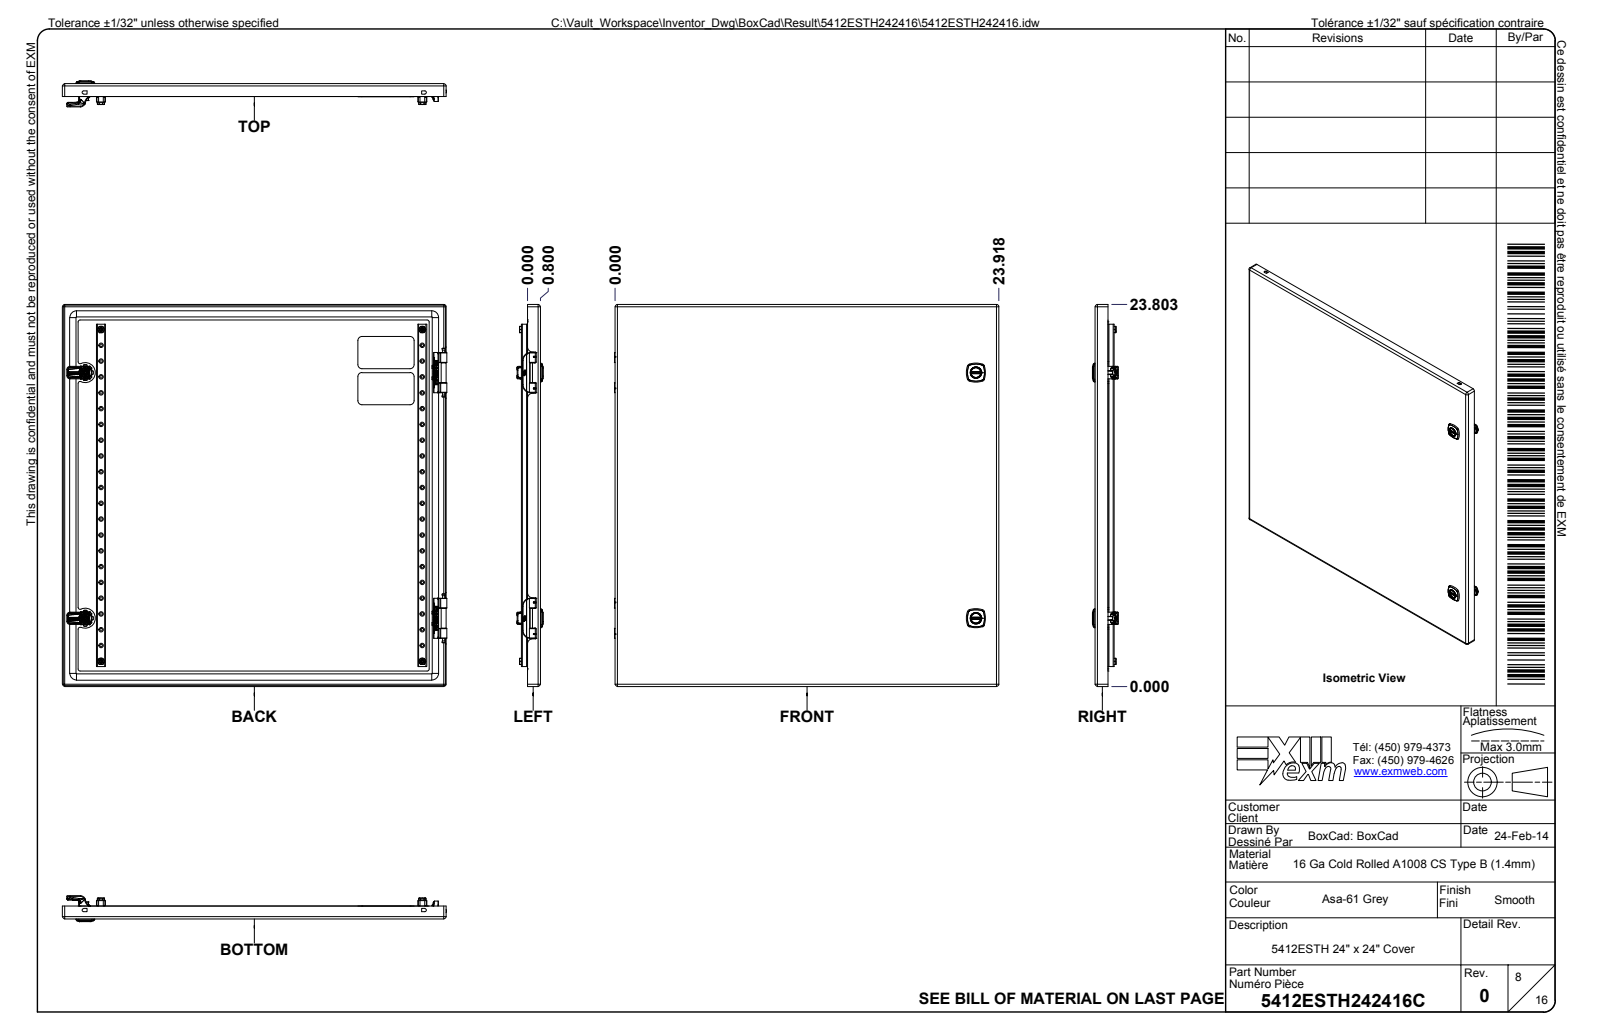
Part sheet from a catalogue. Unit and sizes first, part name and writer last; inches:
Units: inches
Overall size (bounding box): 26.25 × 24.003 × 17.603
Round holes (diameter × count): ⌀0.165 ×40, ⌀0.03 ×10, ⌀0.201 ×10, ⌀0.5 ×10, ⌀0.043 ×8, ⌀0.311 ×6, ⌀0.394 ×6, ⌀0.406 ×6, ⌀0.178 ×4, ⌀0.268 ×4, ⌀0.29 ×4, ⌀0.335 ×4
Round bosses / shafts (diameter × count): ⌀0.237 ×40, ⌀0.232 ×10, ⌀0.03 ×10, ⌀0.256 ×8, ⌀0.039 ×8, ⌀0.289 ×6, ⌀0.177 ×6, ⌀0.748 ×4
Partial cylindrical surfaces — rounded edges, fillets, slot ends (radius × count): R0.02 ×299, R0.008 ×182, R0.01 ×163, R0.039 ×77, R0.125 ×52, R0.012 ×50, R0.031 ×46, R0.059 ×37
Main face-to-face distances: 0.053, 0.75, 0.803, 23.144, 23.894, 23.947, 23.197, 17.081, 17.028, 16.331
Hole centre spacings: 1.969, 21.405, 0.984, 2.953, 15.303, 3.937, 20.25, 20.25
Volume: 2 056 in³ · Surface area: 12 634 in²
Bodies: 87 solids, 14321 faces (4447 planar, 3913 cylindrical, 5961 other)
Part name (STEP PRODUCT): 5412ESTH242416; 5412ESTH242416B; 5412ESTH242416B-P; STK-Q-16005 (+8 more)
STEP written by: Autodesk Inventor 2024 (AUTOMOTIVE_DESIGN)
